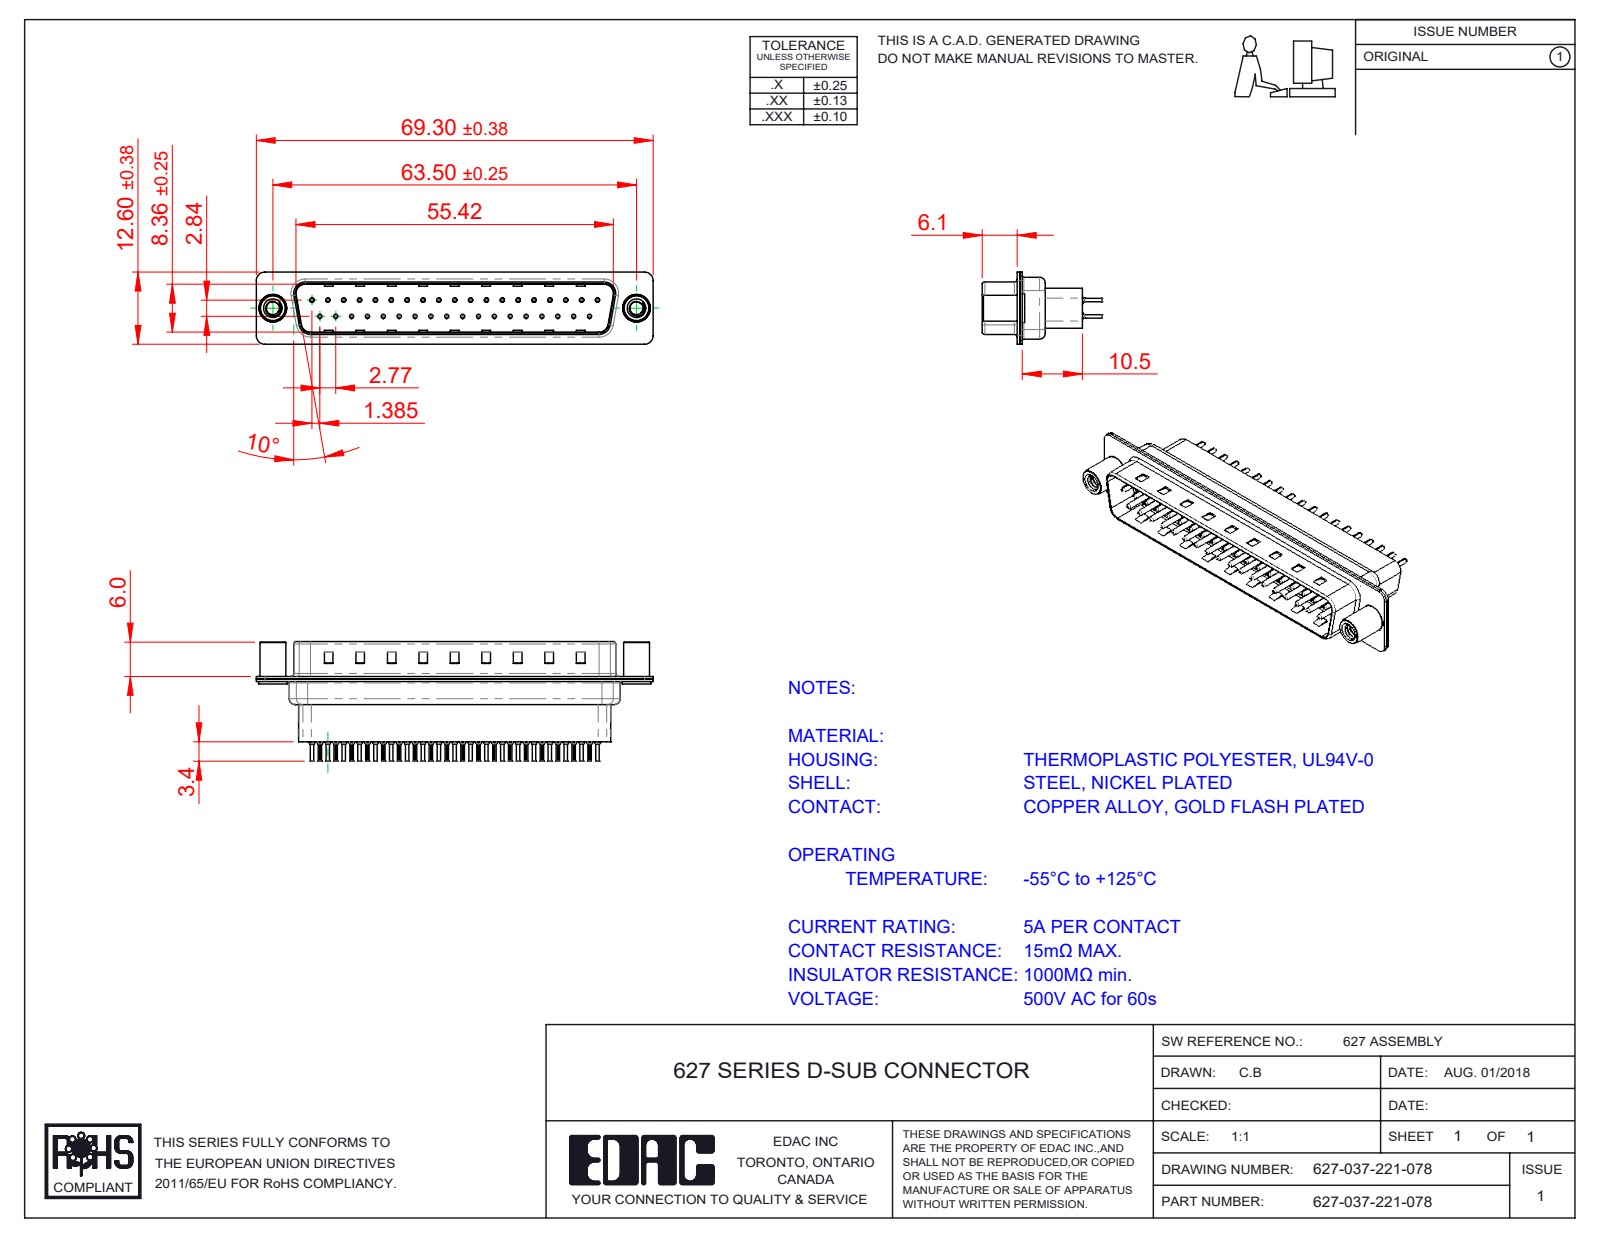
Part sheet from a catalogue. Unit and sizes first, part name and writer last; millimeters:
Units: millimetres
Overall size (bounding box): 69.3 × 20.8 × 12.6
Round holes (diameter × count): ⌀0.2 ×37, ⌀0.35 ×37, ⌀1.1 ×37, ⌀1.6 ×37, ⌀2.26 ×2, ⌀4 ×2, ⌀4.8 ×2
Round bosses / shafts (diameter × count): ⌀2 ×37, ⌀1.5 ×37, ⌀0.75 ×37, ⌀0.6 ×37, ⌀5 ×2, ⌀4.9 ×2, ⌀4.5 ×2
Partial cylindrical surfaces — rounded edges, fillets, slot ends (radius × count): R0.1 ×74, R1.5 ×16, R2 ×12, R0.5 ×8, R1.6 ×8, R0.25 ×4, R0.6 ×4, R0.65 ×4
Main face-to-face distances: 0.4, 0.82, 9.58, 0.68, 7.68, 0.45, 1.5, 1.08, 8.08, 8.76
Hole centre spacings: 3.16, 2.77, 5.54, 8.31, 5.04, 10.1, 11.08, 12.78
Volume: 5 370 mm³ · Surface area: 13 754 mm²
Bodies: 42 solids, 4072 faces (1093 planar, 1538 cylindrical, 1441 other)
Part name (STEP PRODUCT): 627 Shell Front_37 Contacts; 627 Contact Row 2_21H; 627 4-40 Threaded Standoff; 627 Shell Rear_37 Contacts (+3 more)
STEP written by: SolidWorks 2020 (CONFIG_CONTROL_DESIGN)
